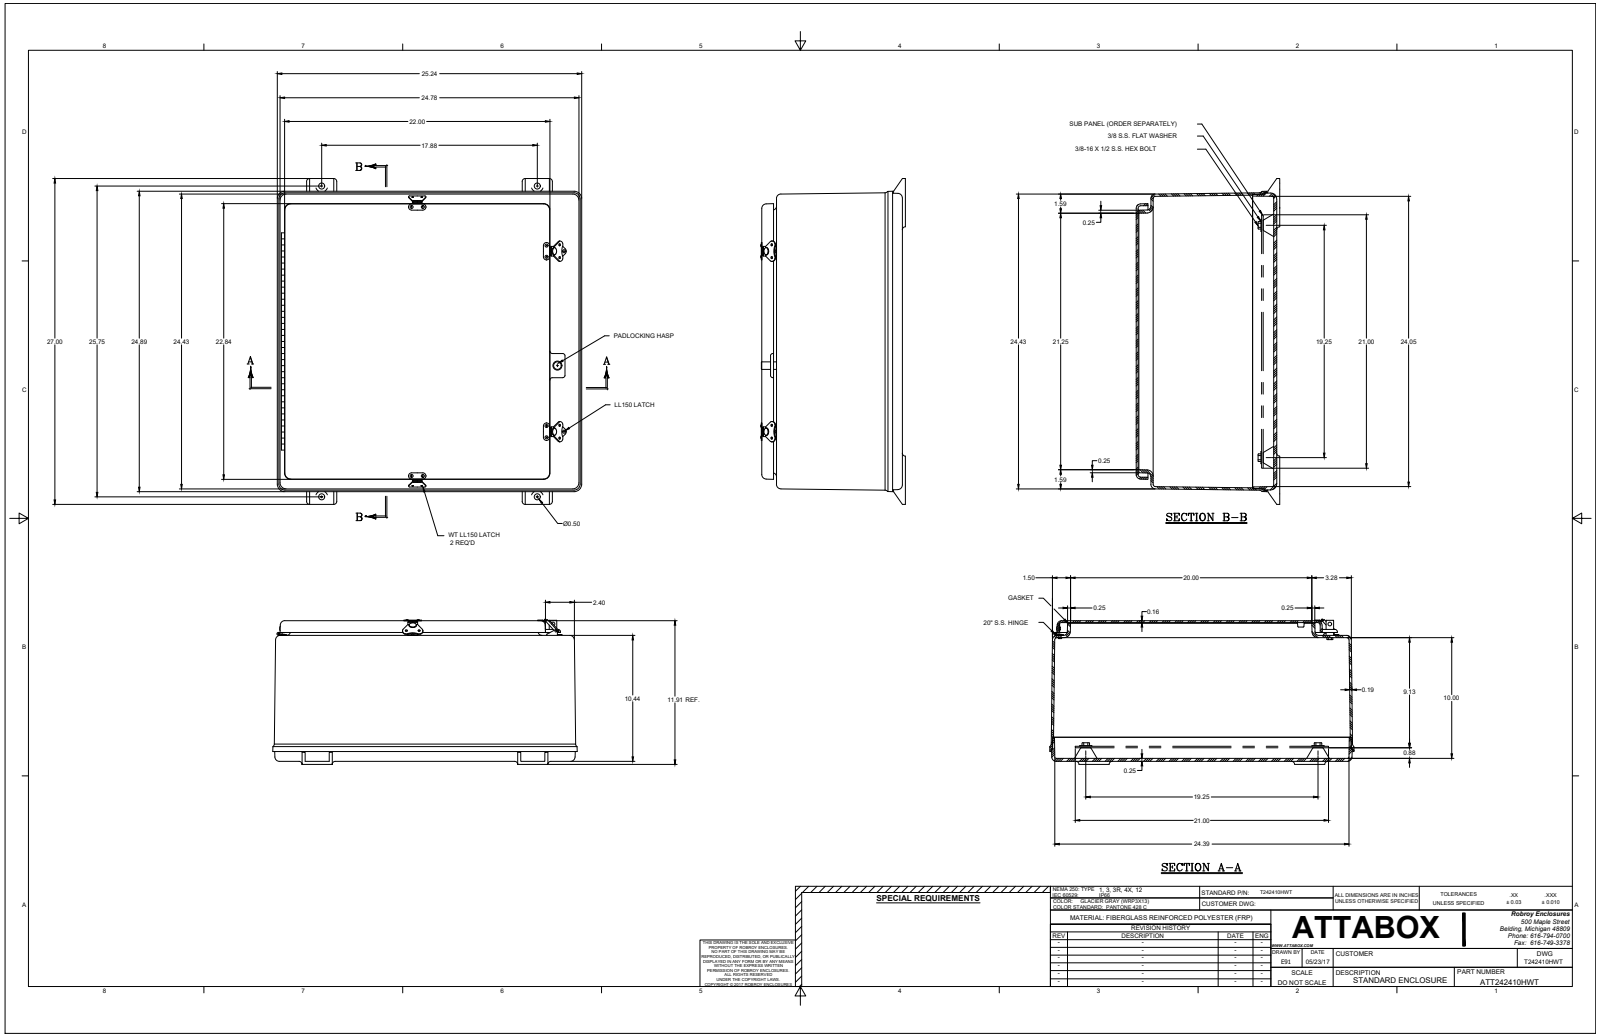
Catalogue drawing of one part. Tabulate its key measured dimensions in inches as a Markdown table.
| quantity | value |
| --- | --- |
| part name | T242410HWT |
| STEP written by | SolidWorks 2018 (AUTOMOTIVE_DESIGN) |
| units | inches |
| bodies | 56 solids, 1502 faces (567 planar, 594 cylindrical, 341 other) |
| overall size | 27 × 25.25 × 12.24 |
| volume | 504.1 in³ |
| surface area | 5 330 in² |
| round holes (diameter × count) | 0.13 × 32, 0.063 × 16, 0.138 × 8, 0.187 × 8, 0.065 × 7, 0.281 × 4, 0.563 × 4, 0.156 × 3, 0.135 × 2, 0.145 × 2, 0.51 × 2, 0.51 × 2 |
| round bosses / shafts (diameter × count) | 0.14 × 16, 0.297 × 8, 0.5 × 4, 0.2 × 3, 0.135 × 2, 0.281 × 1, 0.25 × 1, 0.201 × 1 |
| partial cylindrical surfaces (radius × count) | 0.01 × 101, 0.25 × 24, 0.03 × 16, 0.187 × 12, 0.375 × 12, 0.5 × 12, 0.125 × 10, 0.313 × 10 |
| main face-to-face distances | 0.187, 0.25, 0.156, 11.656, 11.406, 11.5, 11.25, 10.437, 10.25, 10 |
| hole center spacings | 5.25, 11.75, 6.5, 17, 0.736, 1, 1.006, 1.512 |
